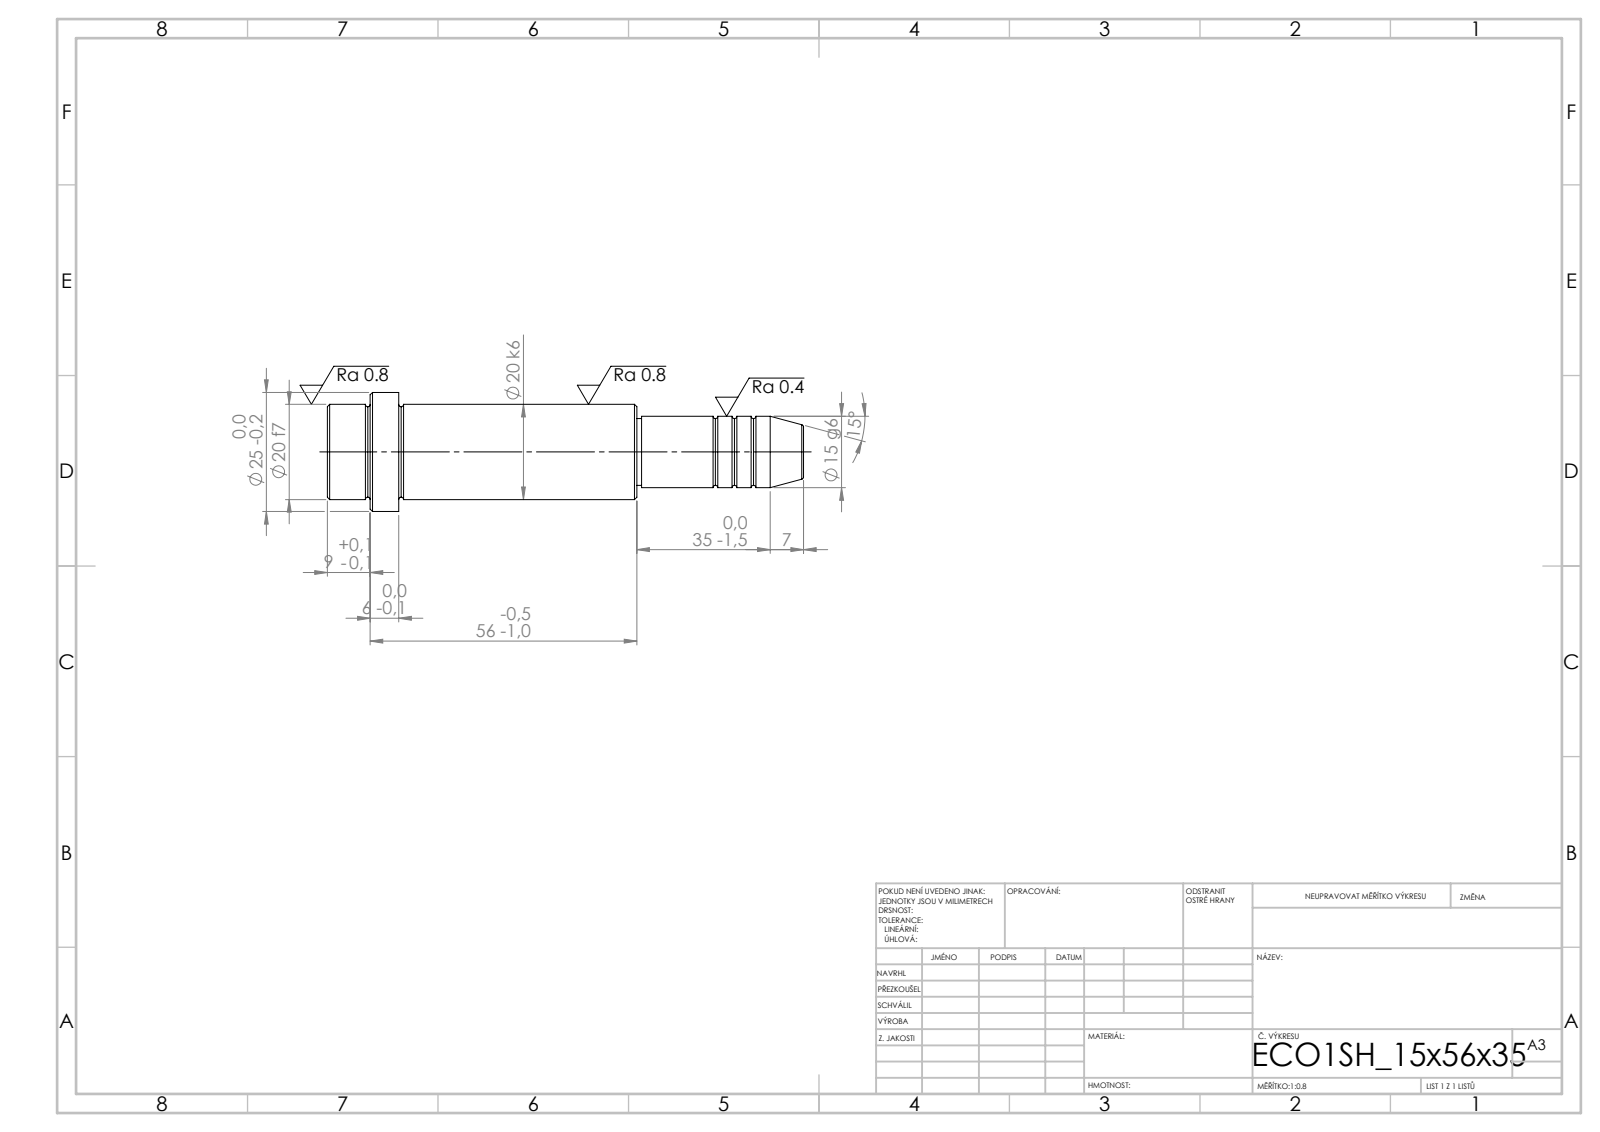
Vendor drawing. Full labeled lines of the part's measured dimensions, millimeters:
STEP written by: SolidWorks 2019 (CONFIG_CONTROL_DESIGN)
Units: millimetres
Bodies: 1 solid, 52 faces (6 planar, 16 cylindrical, 30 other)
Overall size (bounding box): 100 × 25 × 25
Volume: 27 231 mm³ · Surface area: 6 815 mm²
Round bosses / shafts (diameter × count): ⌀25 ×1, ⌀20 ×1, ⌀15 ×1, ⌀14 ×1
Main face-to-face distances: 15, 6, 9, 50, 56, 65, 35, 85, 91, 100
